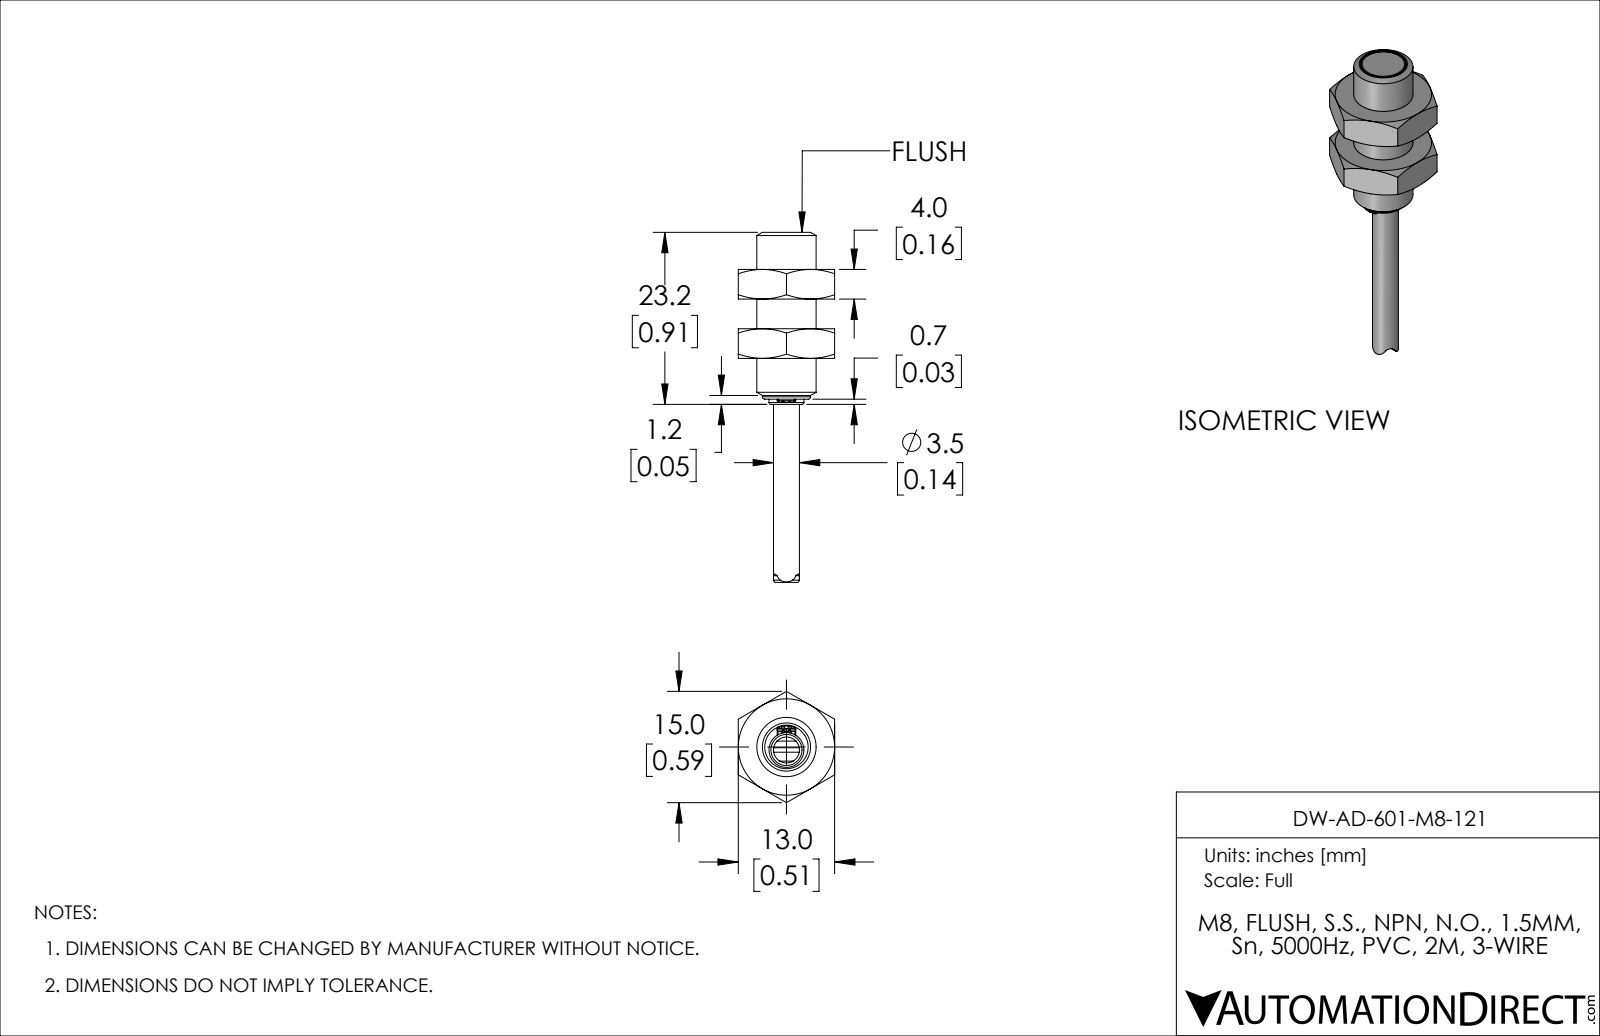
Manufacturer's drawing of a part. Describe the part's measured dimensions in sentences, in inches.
The part is named "DW-AD-601-M8-121". Its 3-D file was written by "SolidWorks 2019 (AUTOMOTIVE_DESIGN)". It is 1 solid with 80 faces: 24 planar, 18 cylindrical and 38 other. Overall it measures 1.858 by 0.591 by 0.512 inches. Its volume is 0.129 cubic inches and its surface area 2.224 square inches. Round bosses or shafts: 1 of diameter 0.315, 1 of diameter 0.256, 1 of diameter 0.185, 1 of diameter 0.138. Partial cylindrical surfaces (rounded edges, fillets, slot ends): 4 of radius 0.005, 2 of radius 0.012, 1 of radius 0.022, 1 of radius 0.03, 1 of radius 0.116, 1 of radius 0.118, 1 of radius 0.177, 1 of radius 0.236. The main face-to-face distances are 0.157, 0.512, 0.315, 0.472, 0.197, 0.354, 0.669, 0.886, 0.689, 0.531.
